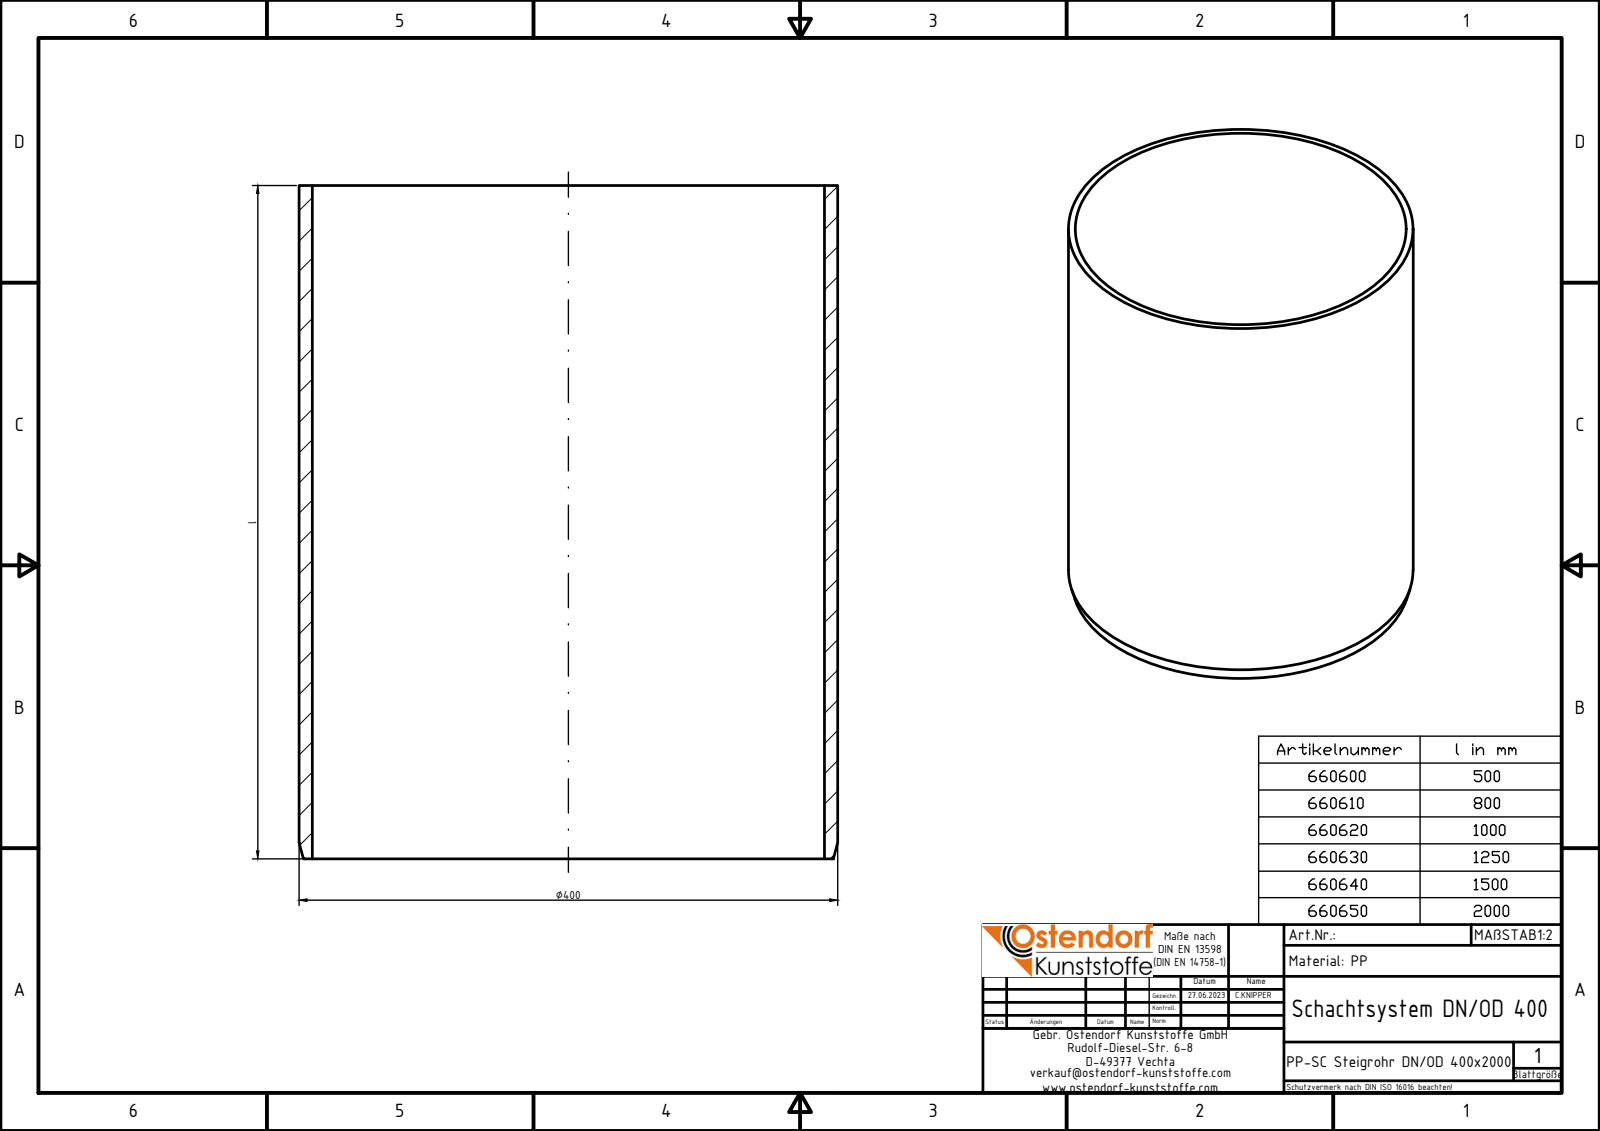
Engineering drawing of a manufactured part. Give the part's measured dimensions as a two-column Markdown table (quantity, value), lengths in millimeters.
| quantity | value |
| --- | --- |
| part name | 660650 |
| STEP written by | Autodesk Inventor 2020 (AUTOMOTIVE_DESIGN) |
| units | millimeters |
| bodies | 1 solid, 5 faces (2 planar, 2 cylindrical, 1 other) |
| overall size | 2000 × 400 × 400 |
| volume | 24 000 000 mm³ |
| surface area | 4 924 000 mm² |
| round holes (diameter × count) | 380.4 × 1 |
| round bosses / shafts (diameter × count) | 400 × 1 |
| main face-to-face distances | 2000 |
